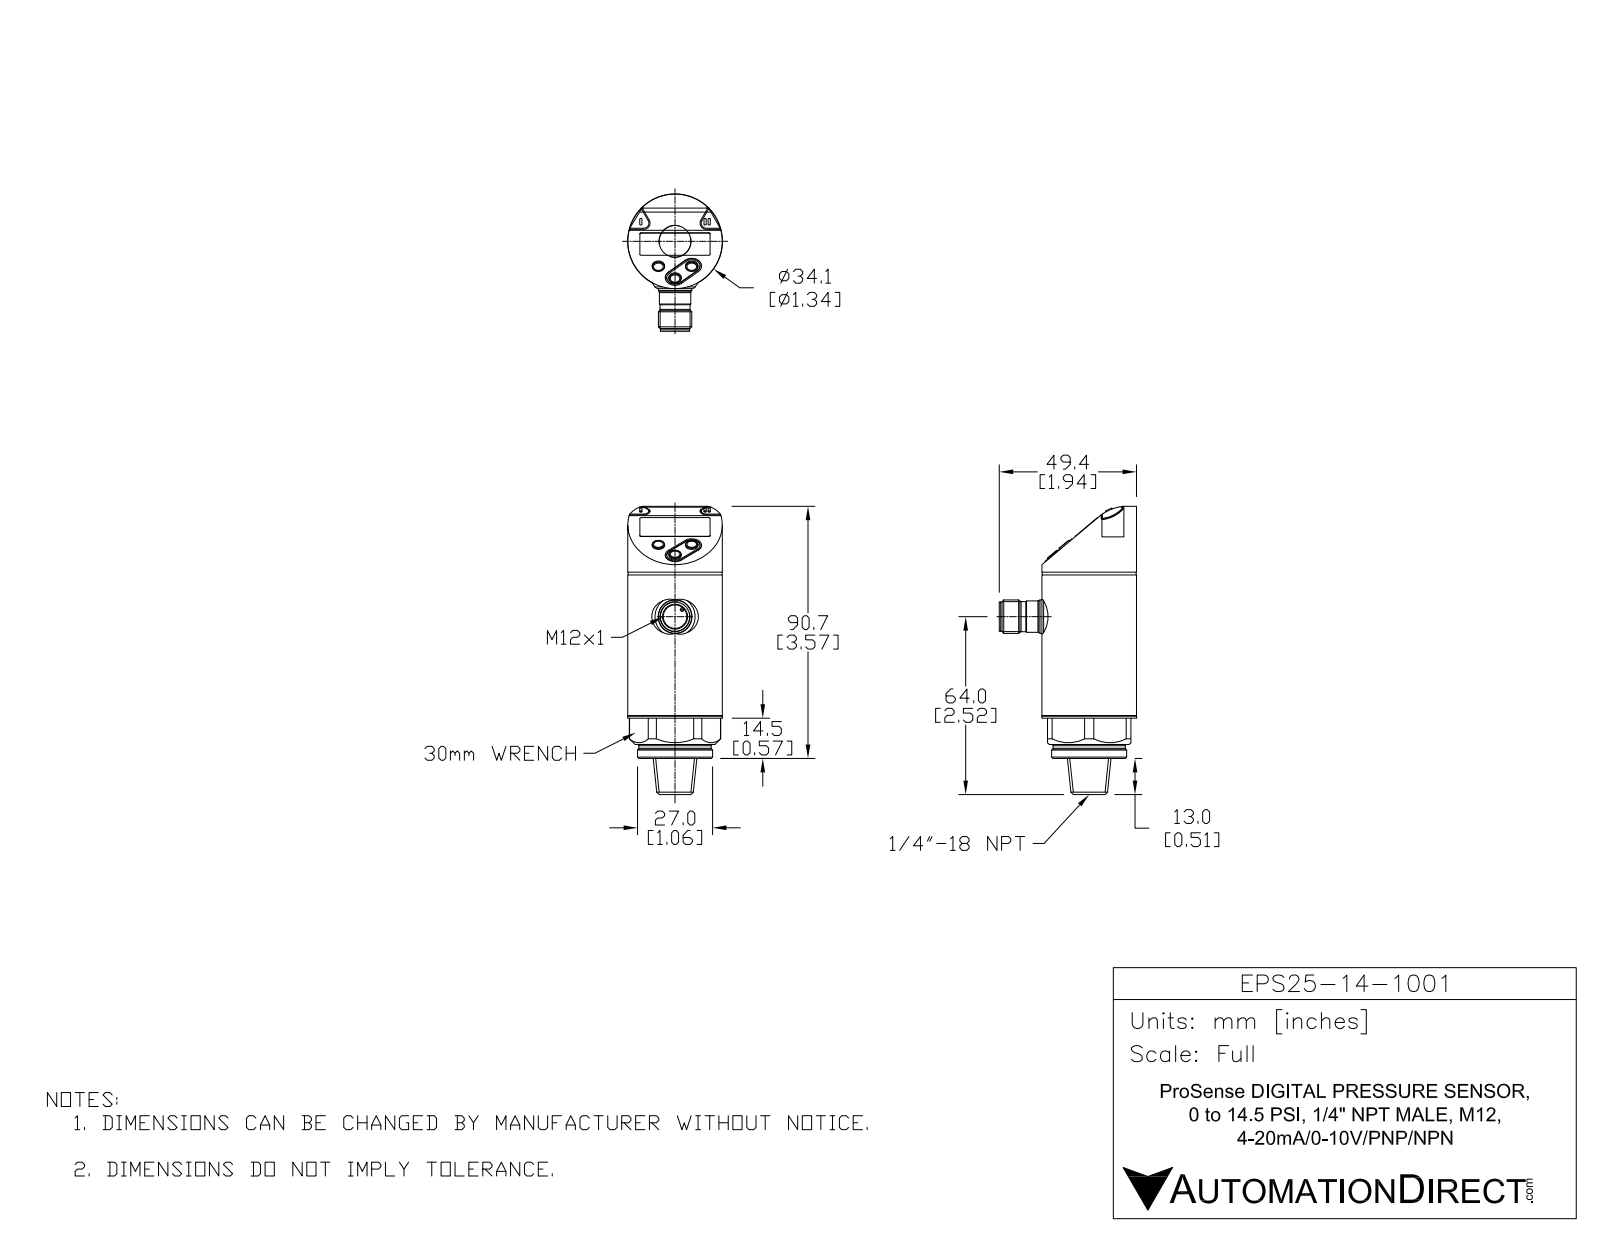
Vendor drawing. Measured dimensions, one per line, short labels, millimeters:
name: EPS25-14-1001
written by: SolidWorks 2016 (AUTOMOTIVE_DESIGN)
unit: mm
bodies: 11 solids, 370 faces (207 planar, 84 cylindrical, 79 other)
size: 103.7 × 49.4 × 34.1
volume: 72 203 mm³; area: 21 365 mm²
holes: 1× ⌀4.2, 1× ⌀8.45
bosses: 4× ⌀1.4, 4× ⌀1, 1× ⌀34.1, 1× ⌀34, 1× ⌀33.8, 1× ⌀27, 1× ⌀26, 1× ⌀12
rounds: 2× R1.8, 2× R2.2, 2× R3, 2× R3.5, 2× R15, 1× R0.61, 1× R6.8, 1× R16.44
face distances: 0.68, 11.5, 12.18, 10.68, 1.5, 10, 2, 2.5, 14, 4
